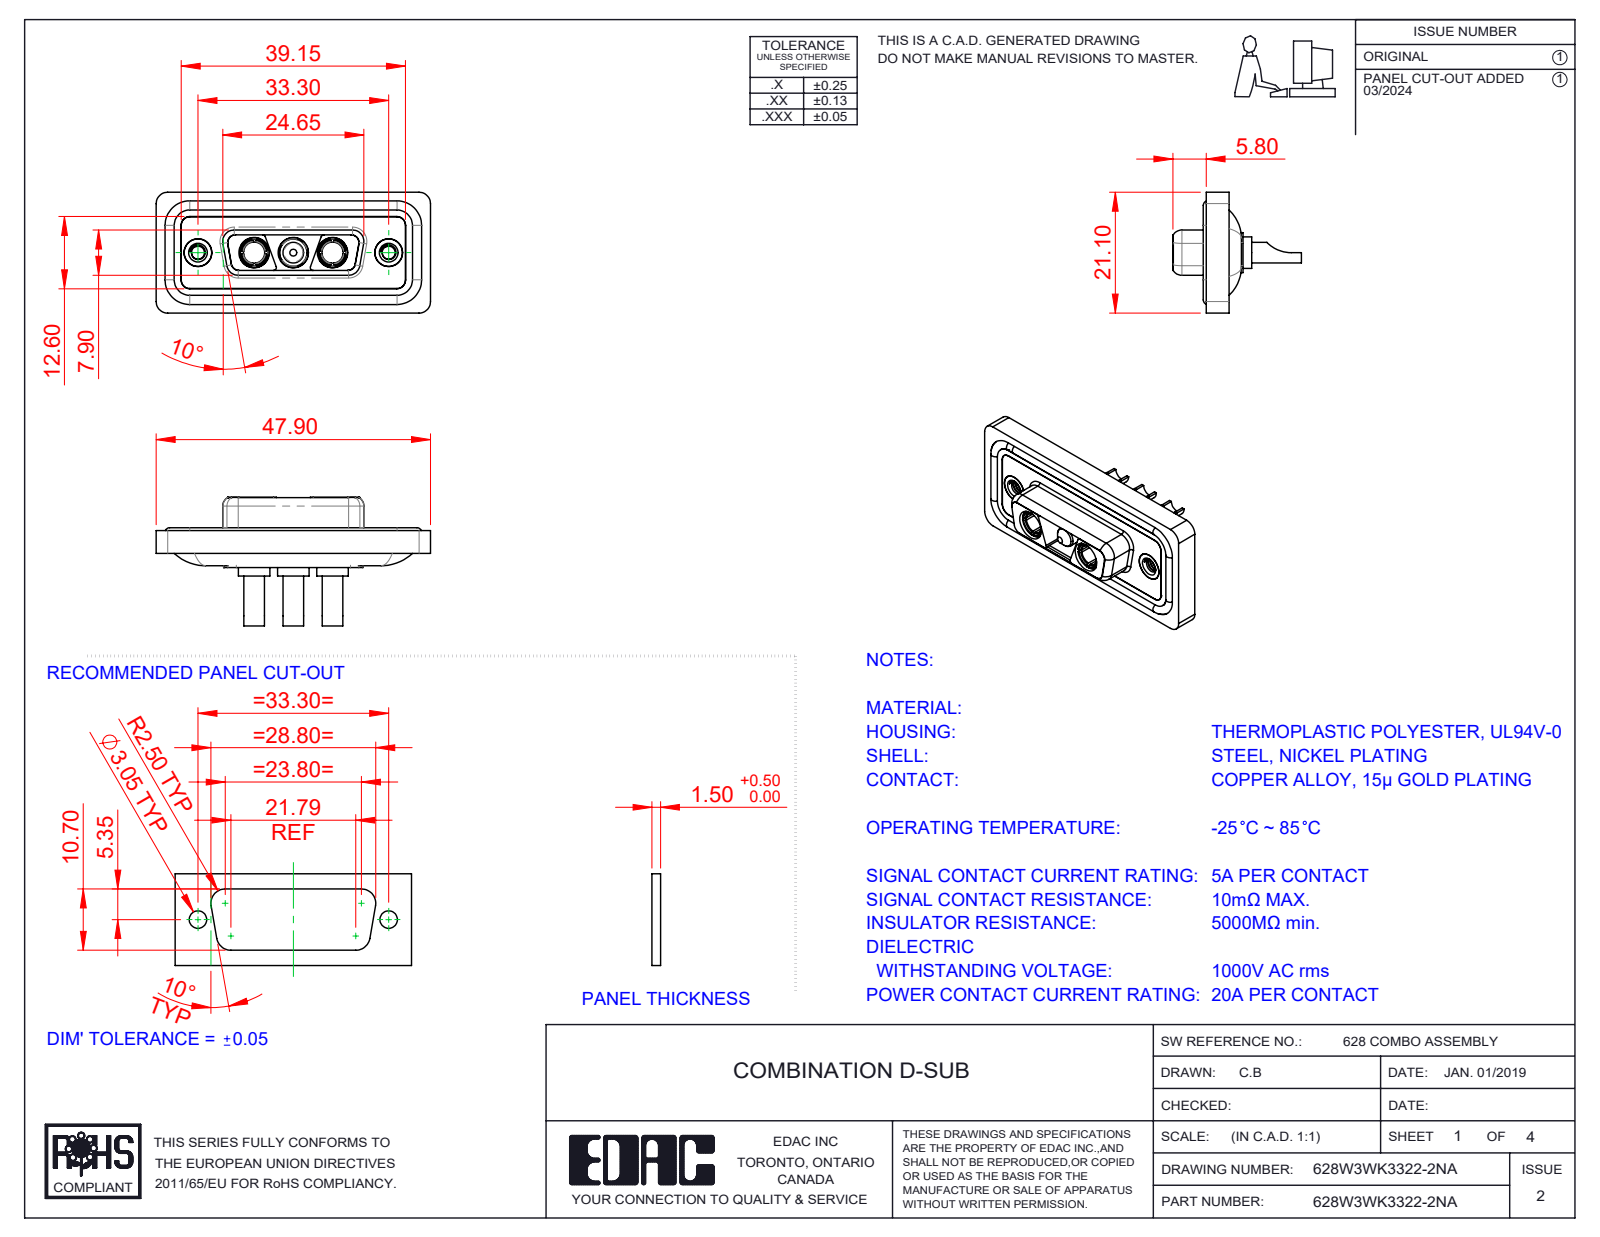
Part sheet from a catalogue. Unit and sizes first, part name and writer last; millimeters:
Units: millimetres
Overall size (bounding box): 47.9 × 22.45 × 21.1
Round holes (diameter × count): ⌀4.85 ×5, ⌀2.7 ×3, ⌀5.3 ×3, ⌀2.26 ×2, ⌀3.7 ×2, ⌀4 ×2, ⌀4.05 ×2, ⌀5 ×2
Round bosses / shafts (diameter × count): ⌀1.6 ×4, ⌀5.5 ×3, ⌀5.2 ×3, ⌀4.75 ×3, ⌀3.75 ×3, ⌀3.6 ×3, ⌀4.96 ×2, ⌀4.95 ×2
Partial cylindrical surfaces — rounded edges, fillets, slot ends (radius × count): R1.5 ×22, R2 ×20, R1.35 ×12, R0.5 ×8, R1.6 ×8, R0.25 ×4, R0.6 ×4, R0.65 ×4
Main face-to-face distances: 0.4, 1.6, 0.5, 1.8, 1.1, 2.9, 5.65, 7.05, 5.35, 1.5
Hole centre spacings: 6.85, 9.8, 16.65, 23.5, 13.7, 33.3
Volume: 5 918 mm³ · Surface area: 9 750 mm²
Bodies: 13 solids, 600 faces (187 planar, 269 cylindrical, 144 other)
Part name (STEP PRODUCT): Power Pin_20A SC; 628Combo Shell Rear_15 Contacts; Power Socket_20A SC; 628W3WK3322-2NA (+4 more)
STEP written by: SolidWorks 2023 (CONFIG_CONTROL_DESIGN)
